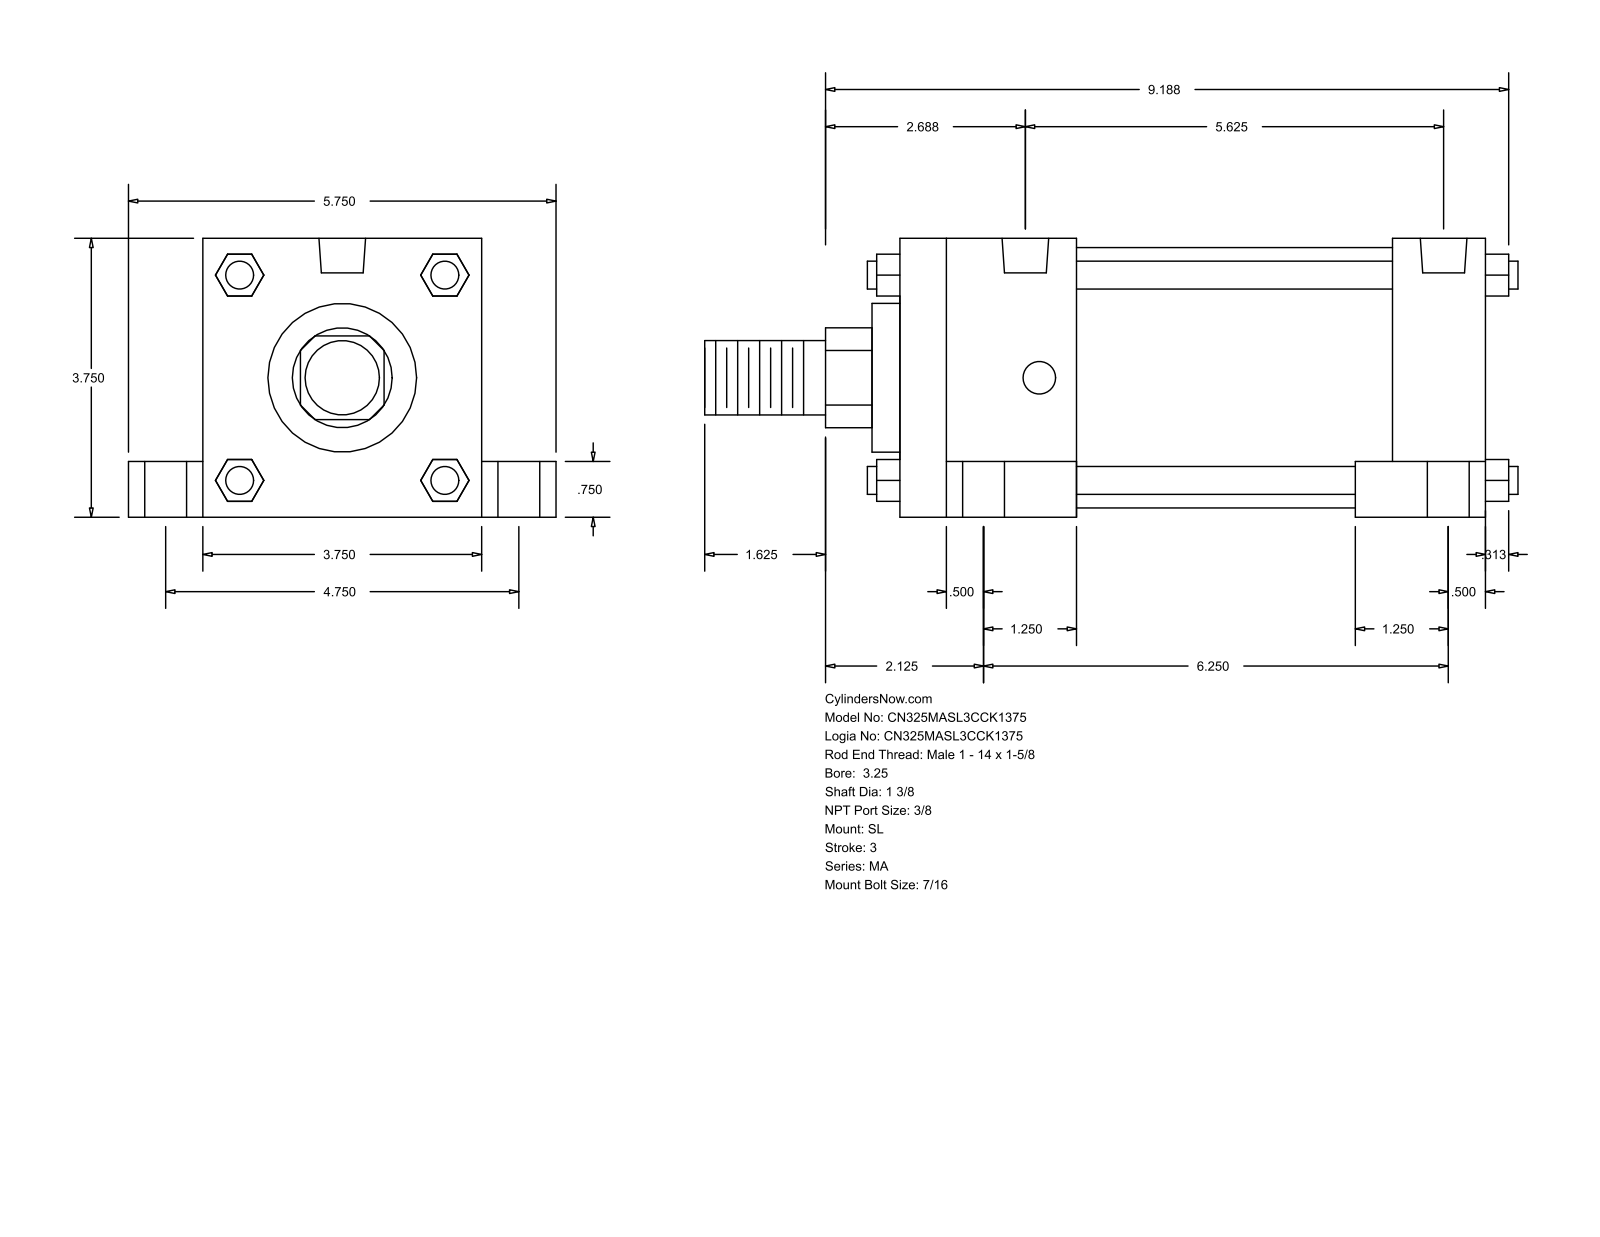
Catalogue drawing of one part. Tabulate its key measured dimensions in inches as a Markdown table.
| quantity | value |
| --- | --- |
| part name | MA_SL__0325_1.375 |
| STEP written by | GSSL Pune (CONFIG_CONTROL_DESIGN) |
| units | inches |
| bodies | 0 solids, 148 faces (112 planar, 36 cylindrical, 0 other) |
| overall size | 10.937 × 5.75 × 3.75 |
| round holes (diameter × count) | 0.437 × 4, 0.563 × 4, 0.813 × 4, 0.627 × 2 |
| round bosses / shafts (diameter × count) | 0.375 × 4, 3.5 × 1, 2 × 1, 1.375 × 1, 1 × 1 |
| partial cylindrical surfaces (radius × count) | 0.672 × 1 |
| main face-to-face distances | 3.75, 7.875, 1, 4.75, 6.625, 1.25, 2.375, 4.25, 5.5, 0.75 |
| hole center spacings | 2.376, 2.388, 2.441, 2.491, 4.75, 5.25, 5.991, 6.163 |
